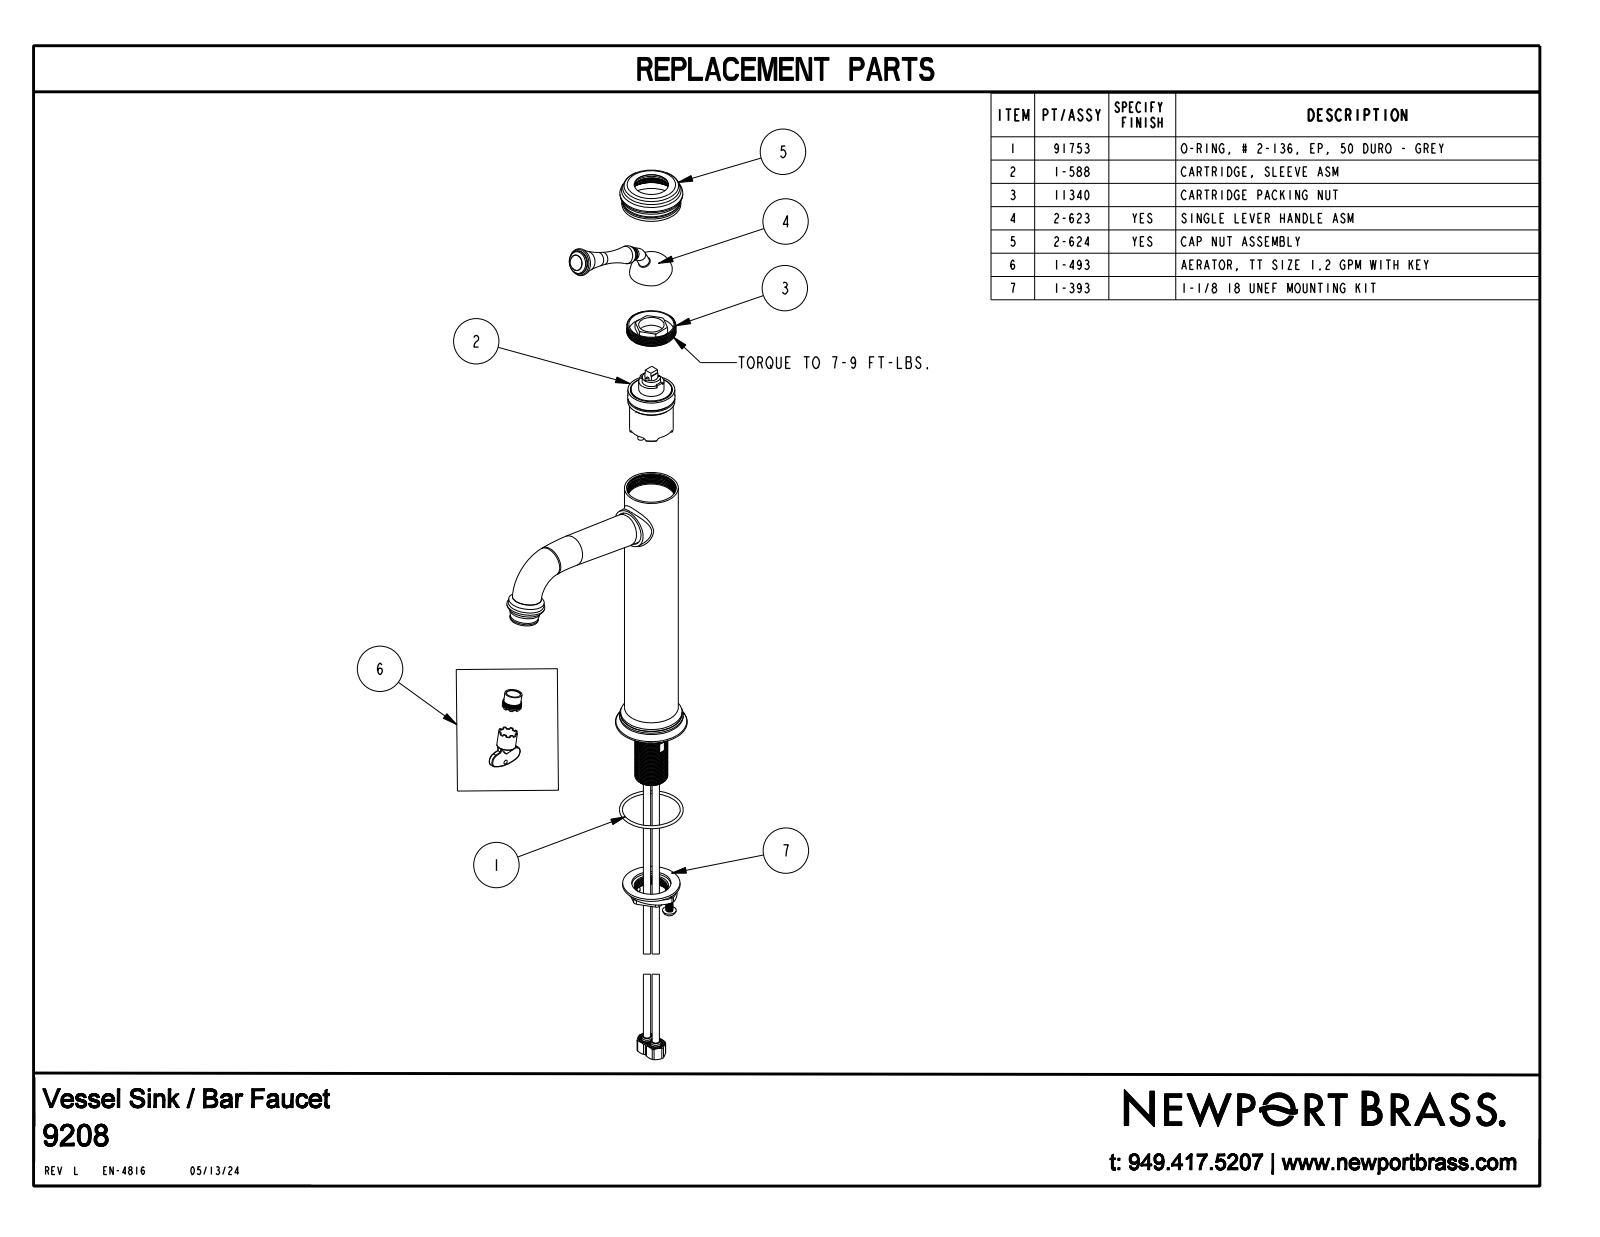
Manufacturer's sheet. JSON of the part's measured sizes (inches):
{"part_name": "9208", "step_written_by": "CREO PARAMETRIC BY PTC INC, 2018400 (AUTOMOTIVE_DESIGN)", "units": "inches", "bodies": {"solids": 1, "faces": 118, "planar": 10, "cylindrical": 18, "other": 90}, "overall_size": [12.498, 7.985, 2.47], "volume_in3": 36.09, "surface_area_in2": 100.3, "round_bosses_or_shafts": [[0.38, 2], [2.11, 1], [1.85, 1], [1.36, 1], [1.23, 1], [1.12, 1], [0.788, 1], [0.47, 1]], "face_to_face_distances": [10.405, 9.566, 0.839, 0.583, 0.379, 9.187, 10.026, 0.833, 0.25]}
